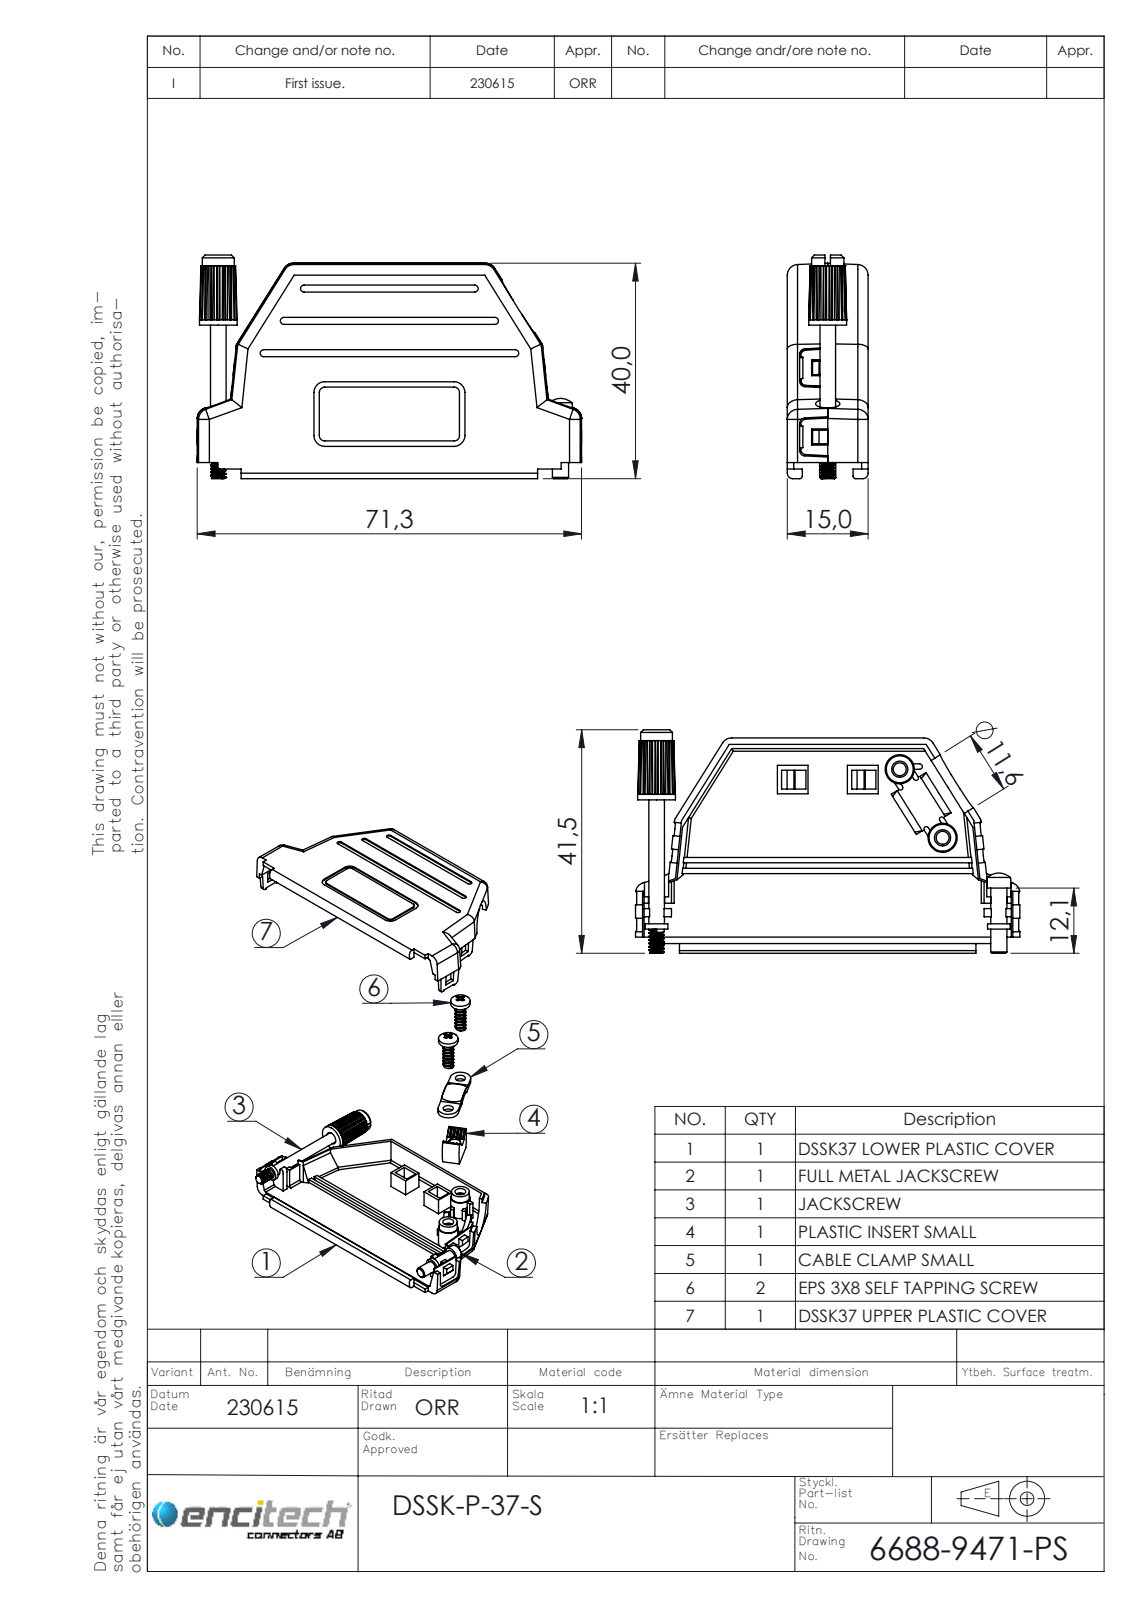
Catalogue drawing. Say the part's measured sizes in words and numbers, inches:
The part is named "6826-0133-04; 6688-9471-PS; 6811-0149-02 Part 2; 6811-0149-02 Part 1 (+4 more)". Its 3-D file was written by "SolidWorks 2021 (AUTOMOTIVE_DESIGN)". It is 10 solids with 960 faces: 624 planar, 256 cylindrical and 80 other. Overall it measures 2.807 by 1.634 by 0.591 inches. Its volume is 0.749 cubic inches and its surface area 26.26 square inches. Round holes: 4 of diameter 0.118, 2 of diameter 0.094, 2 of diameter 0.11, 2 of diameter 0.177, 1 of diameter 0.138, 1 of diameter 0.457. Round bosses or shafts: 2 of diameter 0.215, 2 of diameter 0.213, 2 of diameter 0.197, 2 of diameter 0.165, 2 of diameter 0.097, 1 of diameter 0.276, 1 of diameter 0.236, 1 of diameter 0.173. Partial cylindrical surfaces (rounded edges, fillets, slot ends): 31 of radius 0.079, 28 of radius 0.039, 23 of radius 0.02, 12 of radius 0.026, 4 of radius 0.018, 2 of radius 0.018, 2 of radius 0.024, 2 of radius 0.035. The main face-to-face distances are 0.067, 0.524, 0.591, 0.457, 0.295, 0.512, 0.039, 0.579, 0.228, 0.059. The hole center spacings are 0.292, 0.299, 0.591, 2.5.
